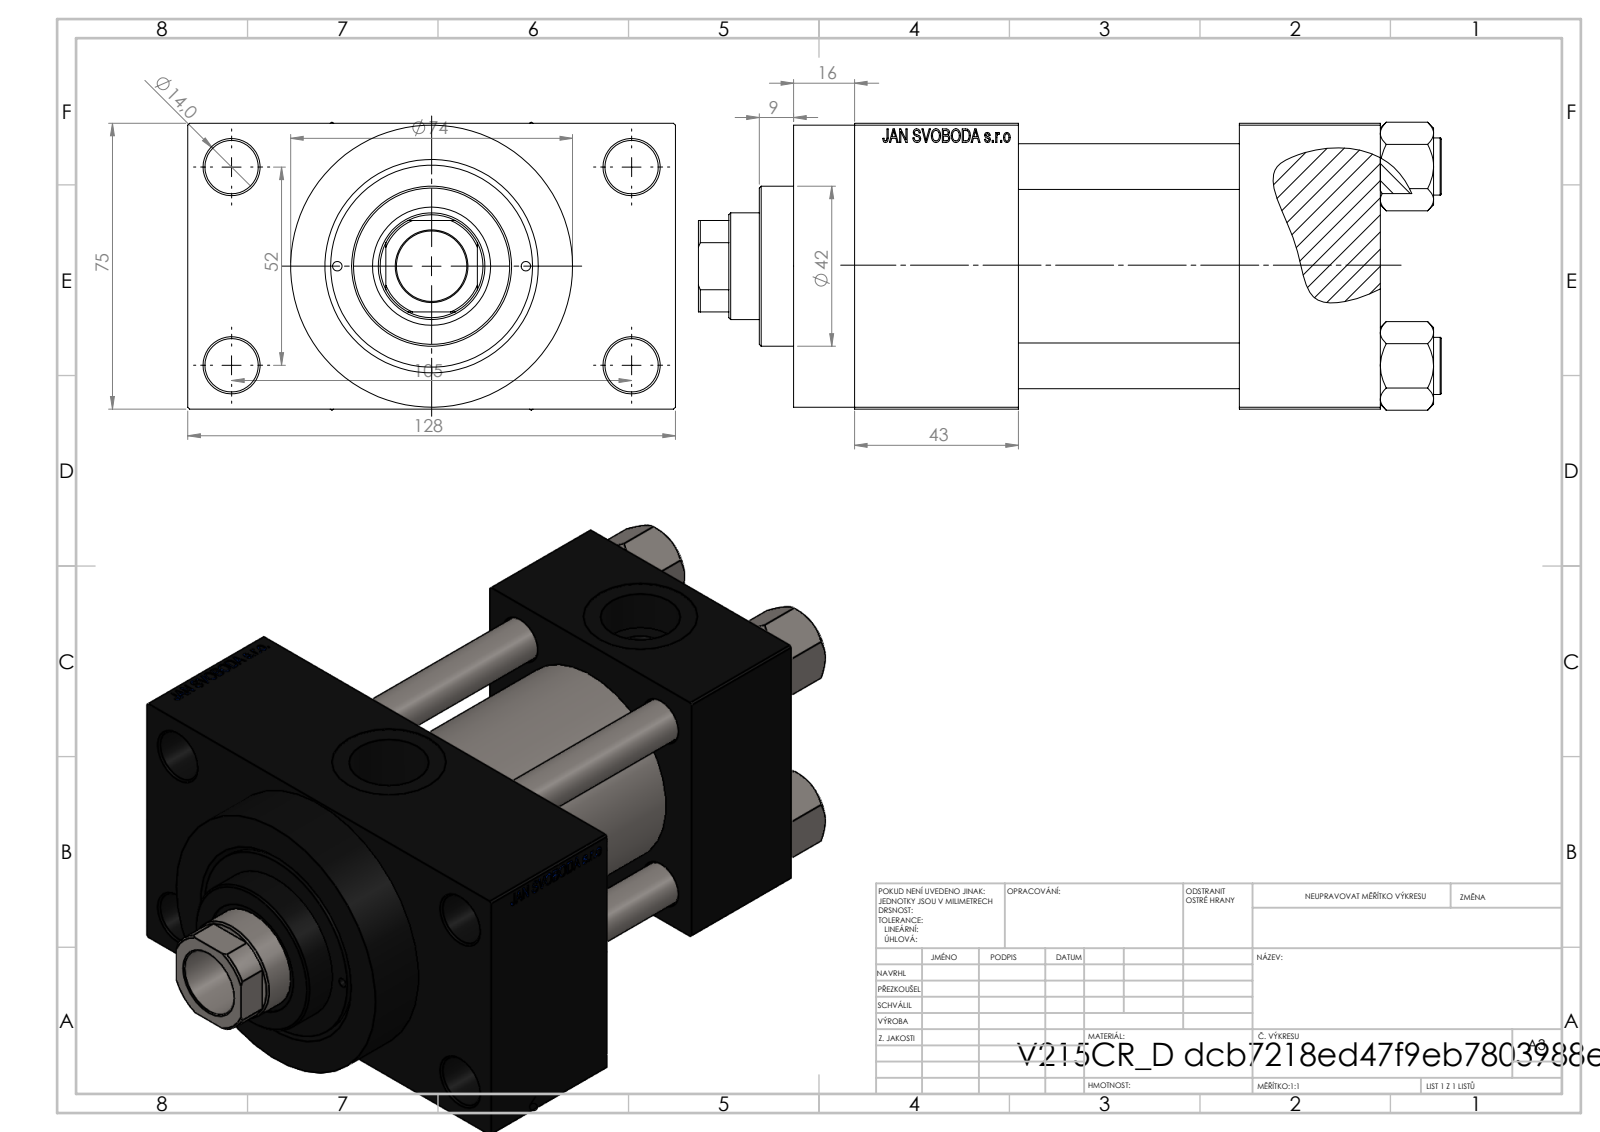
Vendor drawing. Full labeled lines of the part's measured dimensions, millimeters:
Part name (STEP PRODUCT): V215CR_D_TYCINKA; V215CR_D_Body; V215CR_VCP_D; V215_VC_A (+1 more)
STEP written by: SolidWorks 2019 (CONFIG_CONTROL_DESIGN)
Units: millimetres
Bodies: 11 solids, 1112 faces (499 planar, 93 cylindrical, 520 other)
Overall size (bounding box): 195 × 128 × 75.54
Volume: 814 991 mm³ · Surface area: 168 804 mm²
Round holes (diameter × count): ⌀12 ×4, ⌀14 ×4, ⌀2.5 ×2, ⌀7 ×2, ⌀20.96 ×2, ⌀30 ×2, ⌀18.5 ×1, ⌀28 ×1, ⌀31 ×1, ⌀41 ×1, ⌀50 ×1, ⌀53 ×1
Round bosses / shafts (diameter × count): ⌀15 ×4, ⌀74 ×1, ⌀56 ×1, ⌀42 ×1
Partial cylindrical surfaces — rounded edges, fillets, slot ends (radius × count): R13.5 ×1
Main face-to-face distances: 75, 58, 37, 95, 26.5, 101.5, 138, 101, 43, 16
Hole centre spacings: 26.19, 26.35, 36.98, 38.03, 52.3, 57.22, 58.43, 58.59
